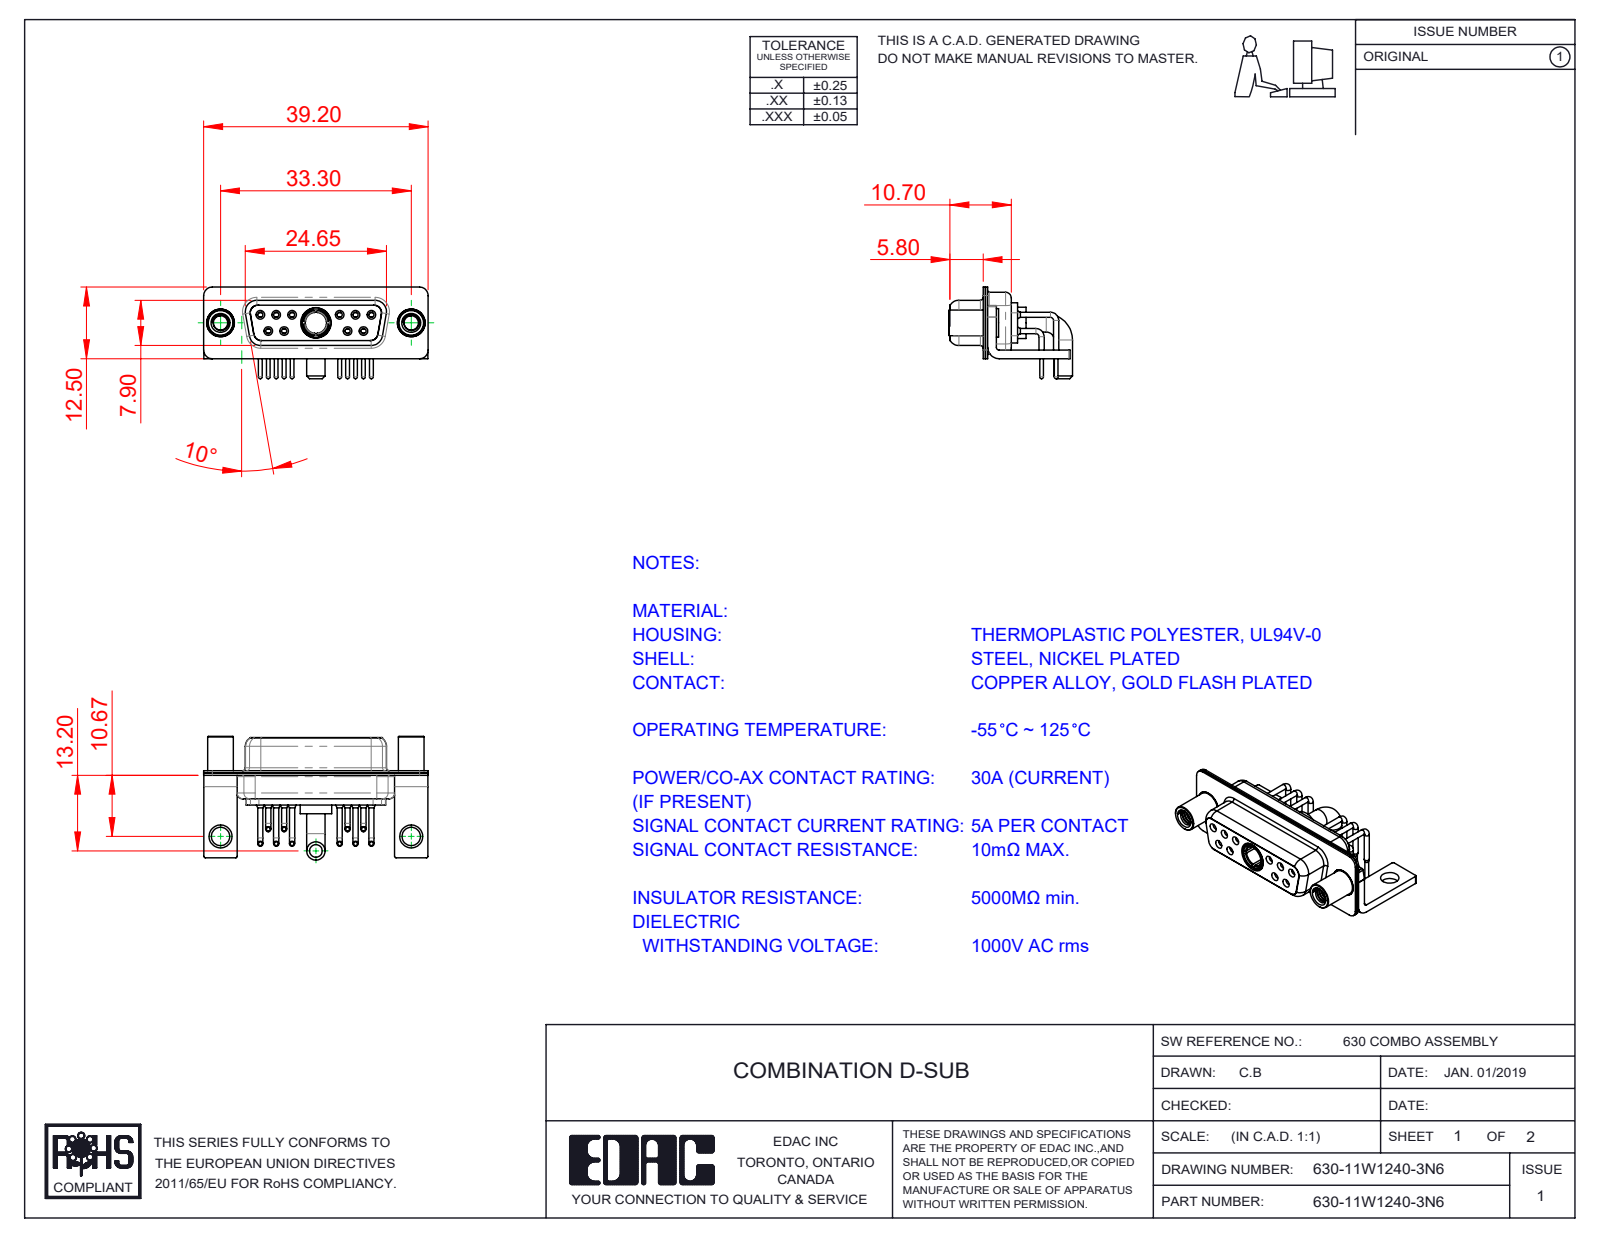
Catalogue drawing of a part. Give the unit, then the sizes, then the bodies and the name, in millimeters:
Units: millimetres
Overall size (bounding box): 39.2 × 21.6 × 16
Round holes (diameter × count): ⌀0.9 ×10, ⌀1.1 ×10, ⌀1.5 ×10, ⌀2 ×10, ⌀1.7 ×6, ⌀1.6 ×4, ⌀4.85 ×3, ⌀2.5 ×2, ⌀3.2 ×2, ⌀4 ×2, ⌀4.05 ×2, ⌀3.7 ×1
Round bosses / shafts (diameter × count): ⌀0.9 ×10, ⌀0.65 ×10, ⌀1.6 ×6, ⌀5 ×2, ⌀4.95 ×2, ⌀4.8 ×2, ⌀4.5 ×2, ⌀3.2 ×2
Partial cylindrical surfaces — rounded edges, fillets, slot ends (radius × count): R0.25 ×16, R1.5 ×16, R2 ×13, R1.35 ×12, R1.6 ×8, R0.5 ×5, R0.6 ×4, R0.65 ×4
Main face-to-face distances: 0.4, 0.8, 1.4, 0.45, 8.45, 1.5, 1.8, 8.9, 6.2, 2.3
Hole centre spacings: 3.16, 2.77, 13.85, 11.08, 16.62, 5.03, 5.04, 5.54
Volume: 3 058 mm³ · Surface area: 7 215 mm²
Bodies: 19 solids, 985 faces (268 planar, 464 cylindrical, 253 other)
Part name (STEP PRODUCT): 630Combo Contact Row 1; 630Combo Contact Row 2; 630-11W1240-3N6; 630Combo Threaded Standoff_D (+5 more)
STEP written by: SolidWorks 2020 (CONFIG_CONTROL_DESIGN)
